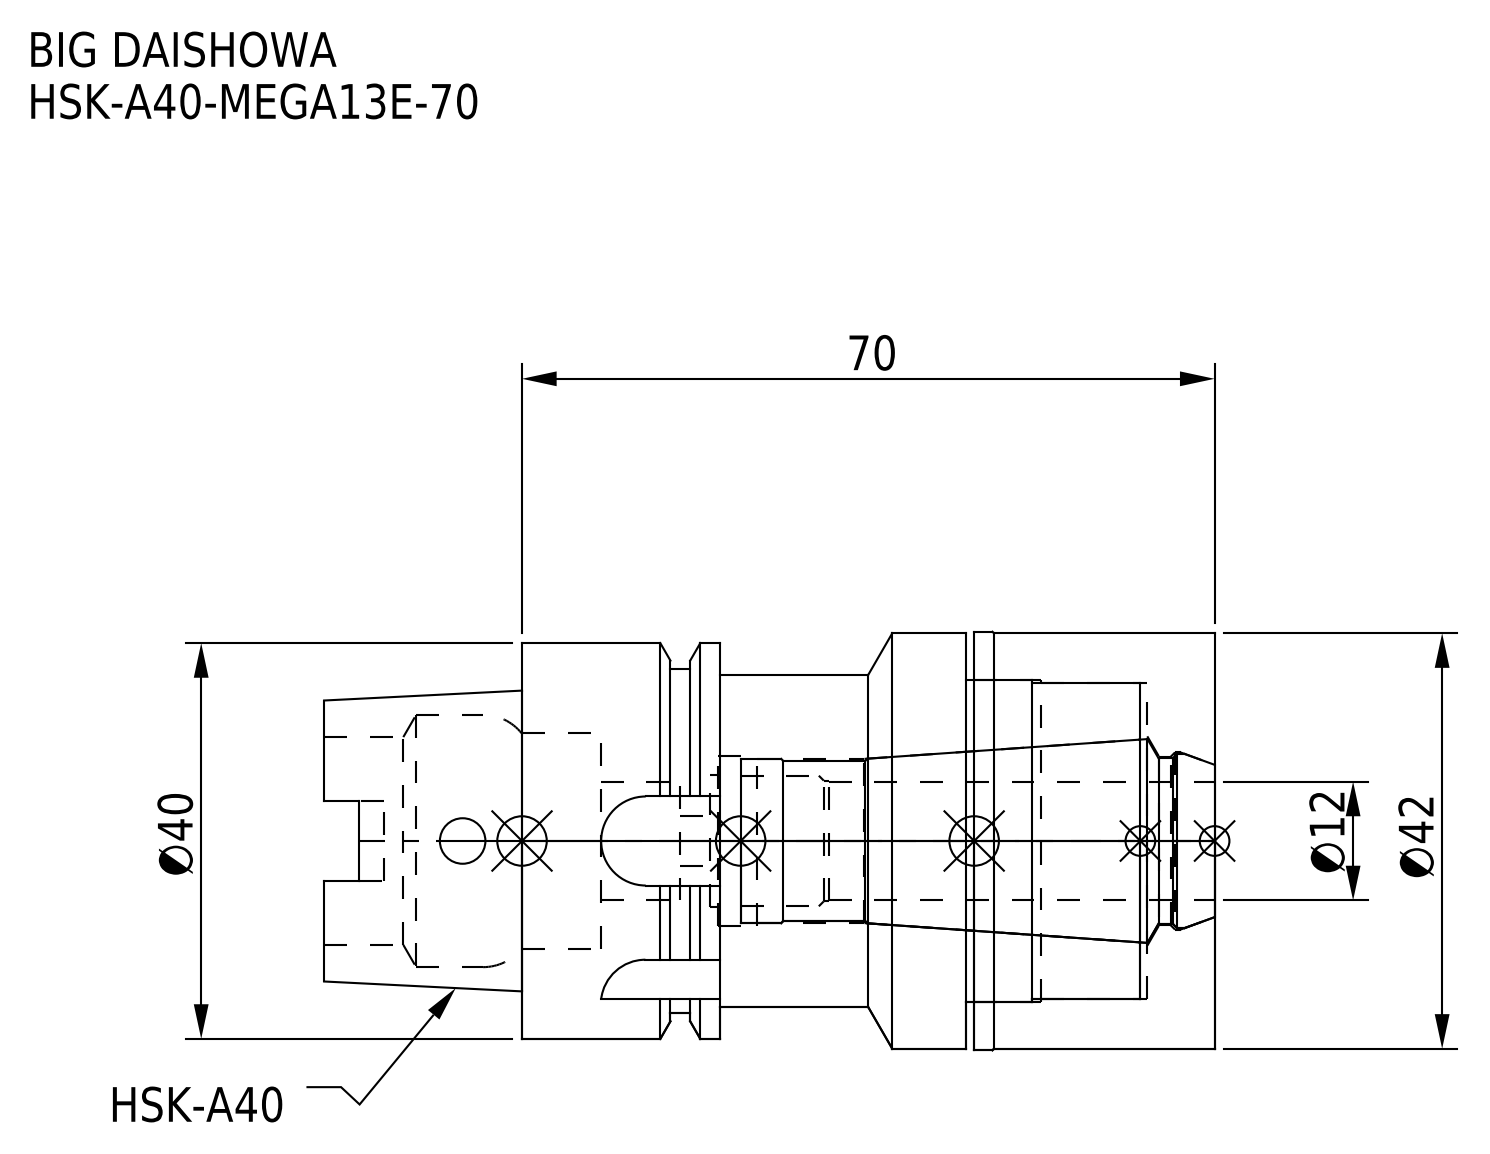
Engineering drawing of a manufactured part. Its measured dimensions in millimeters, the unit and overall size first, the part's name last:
Units: millimetres
Overall size (bounding box): 90 × 42.3 × 42.3
Round holes (diameter × count): ⌀4.6 ×1, ⌀5 ×1, ⌀12 ×1, ⌀13.3 ×1, ⌀16.6 ×1, ⌀17 ×1, ⌀17.2 ×1, ⌀17.9 ×1, ⌀21 ×1, ⌀21.8 ×1, ⌀25.5 ×1, ⌀32 ×1
Round bosses / shafts (diameter × count): ⌀42.3 ×1, ⌀42 ×1, ⌀40 ×1, ⌀34.8 ×1, ⌀33.6 ×1
Partial cylindrical surfaces — rounded edges, fillets, slot ends (radius × count): R1.88 ×4, R4.5 ×4
Main face-to-face distances: 25.1, 0.8, 24.3, 70, 45.7, 44.9, 6.8, 17.5, 7.5, 20
Volume: 71 998 mm³ · Surface area: 25 008 mm²
Bodies: 2 solids, 129 faces (45 planar, 58 cylindrical, 26 other)
Part name (STEP PRODUCT): MEN13_1.stp; HSK-A40-MEGA13E-70_1.stp; HSK-A40-MEGA13E-70-120.stp; HSK-A40-MEGA13E-70 (+3 more)
STEP written by: SolidWorks 2019 (CONFIG_CONTROL_DESIGN)
